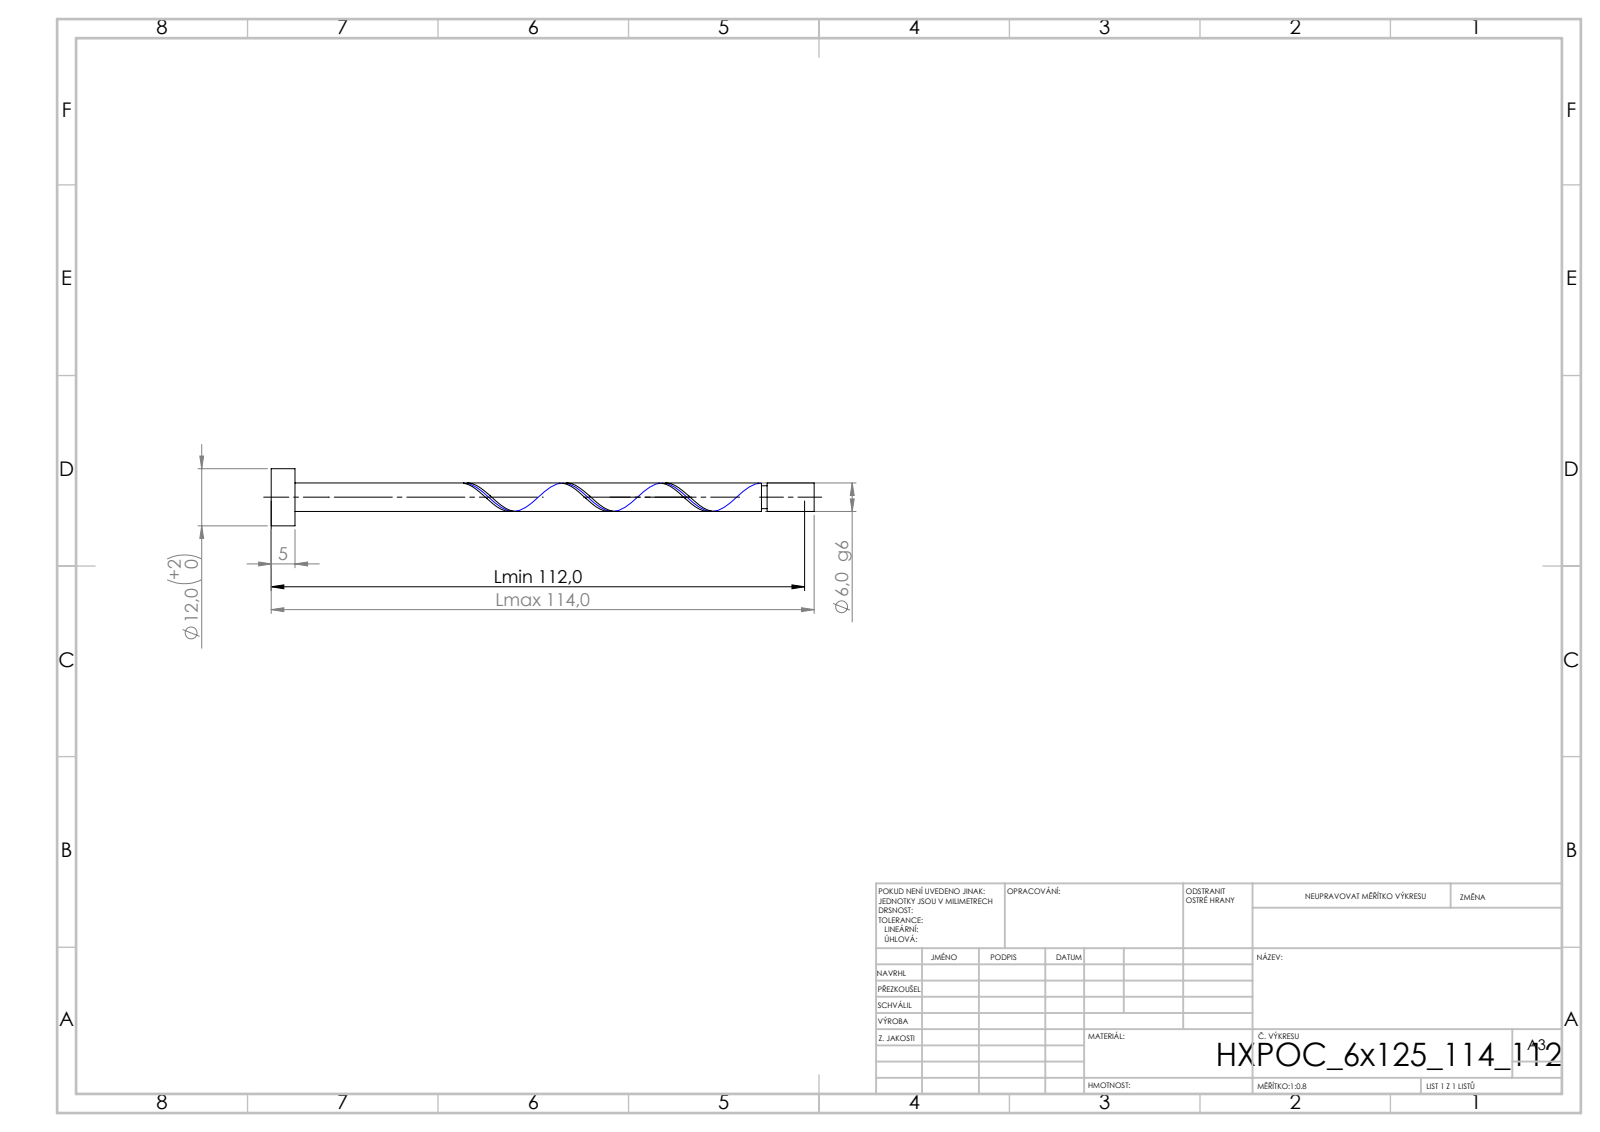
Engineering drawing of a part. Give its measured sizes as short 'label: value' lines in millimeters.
written by: SolidWorks 2019 (CONFIG_CONTROL_DESIGN)
unit: mm
bodies: 1 solid, 21 faces (6 planar, 14 cylindrical, 1 other)
size: 114 × 12 × 12
volume: 3 601 mm³; area: 2 539 mm²
bosses: 1× ⌀12, 1× ⌀6, 1× ⌀4.8
face distances: 5, 114, 109, 104.14, 99.14, 9.86, 102.94, 97.94, 1.2, 11.06
